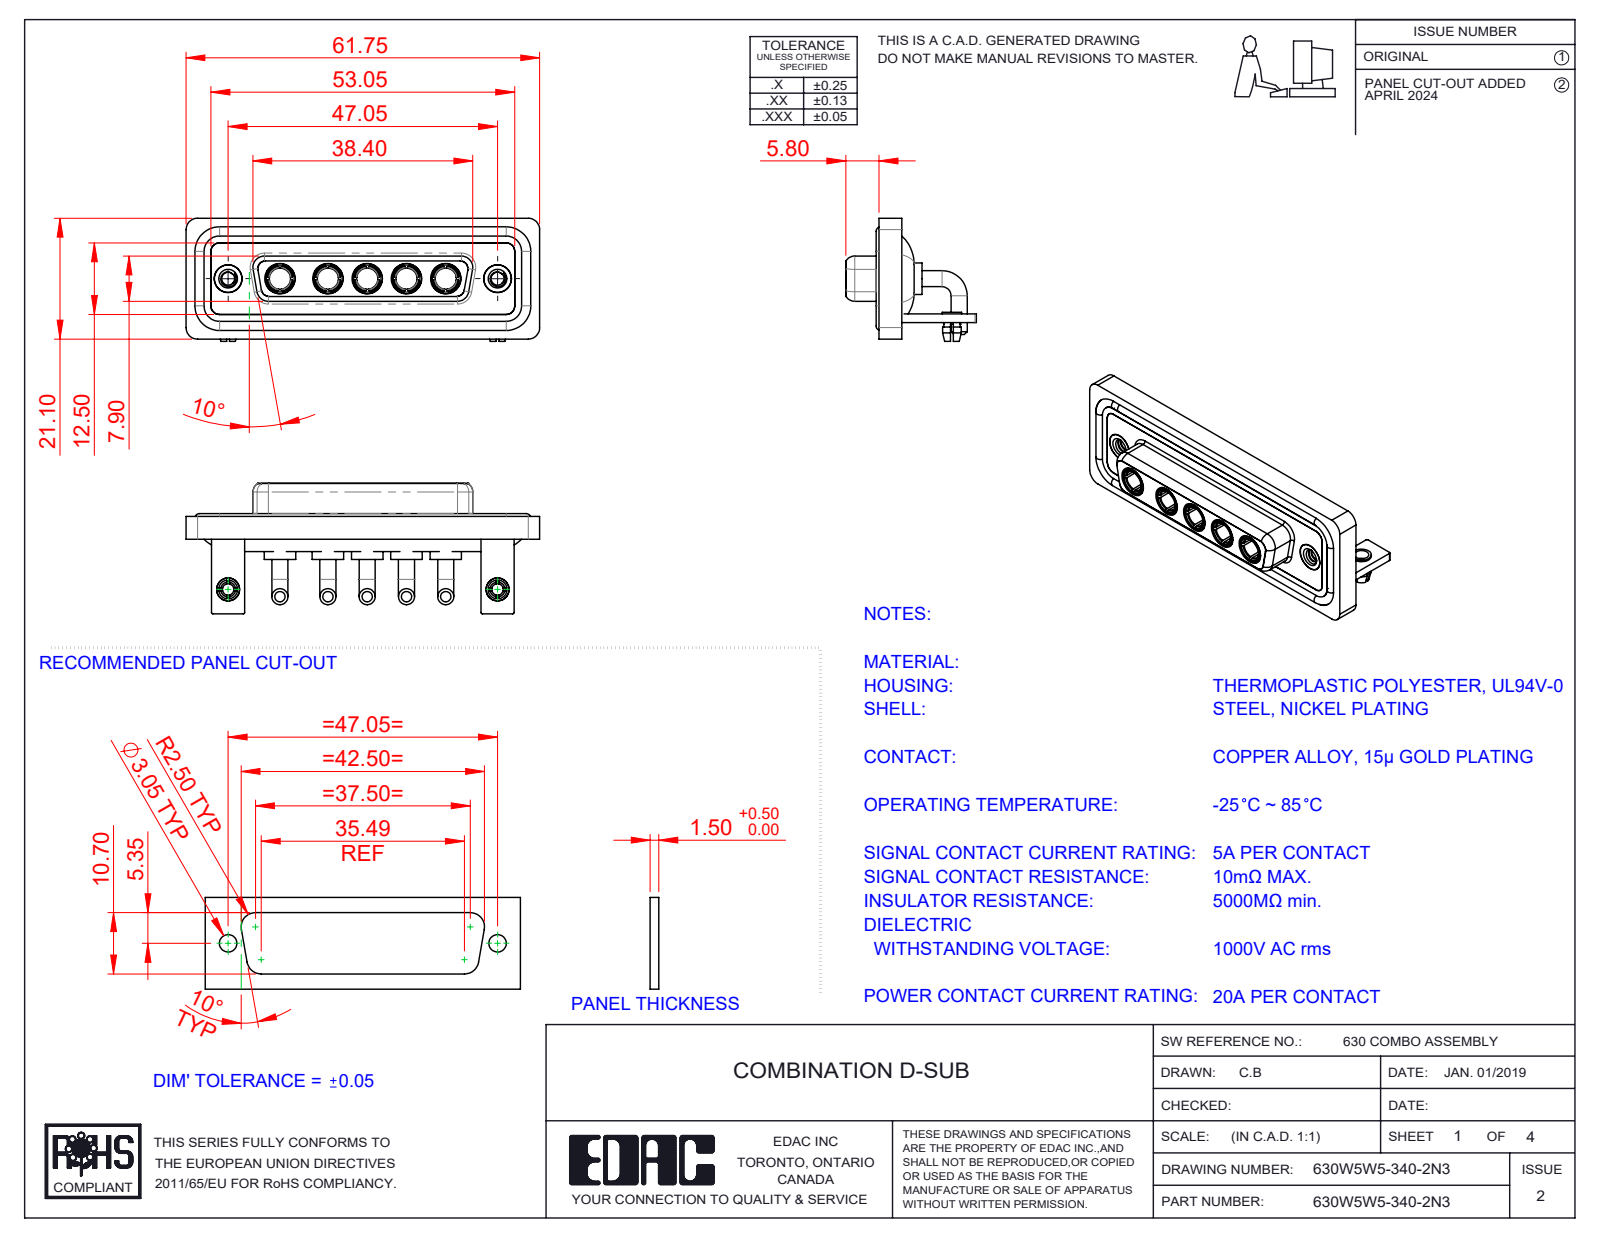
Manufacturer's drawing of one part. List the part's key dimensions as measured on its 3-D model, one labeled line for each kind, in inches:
Part name (STEP PRODUCT): 630Combo Board Lock_50 Contacts; 630Combo Shell Front_25 Contacts; Power Socket_20A RA; 630Combo Housing_5W5 (+5 more)
STEP written by: SolidWorks 2023 (CONFIG_CONTROL_DESIGN)
Units: inches
Bodies: 21 solids, 916 faces (318 planar, 369 cylindrical, 229 other)
Overall size (bounding box): 2.431 × 0.898 × 0.846
Volume: 0.539 in³ · Surface area: 22.88 in²
Round holes (diameter × count): ⌀0.191 ×7, ⌀0.146 ×5, ⌀0.209 ×5, ⌀0.079 ×2, ⌀0.089 ×2, ⌀0.098 ×2, ⌀0.126 ×2, ⌀0.157 ×2, ⌀0.159 ×2, ⌀0.197 ×2
Round bosses / shafts (diameter × count): ⌀0.11 ×10, ⌀0.217 ×5, ⌀0.205 ×5, ⌀0.195 ×5, ⌀0.187 ×5, ⌀0.148 ×5, ⌀0.063 ×4, ⌀0.195 ×2
Partial cylindrical surfaces — rounded edges, fillets, slot ends (radius × count): R0.079 ×19, R0.059 ×18, R0.01 ×16, R0.053 ×8, R0.063 ×8, R0.02 ×5, R0.083 ×5, R0.024 ×4
Main face-to-face distances: 0.016, 0.071, 0.114, 0.059, 0.146, 0.161, 0.043, 0.055, 0.063, 0.098
Hole centre spacings: 0.27, 0.356, 1.496, 1.852, 0.27, 0.33, 0.54, 0.541
